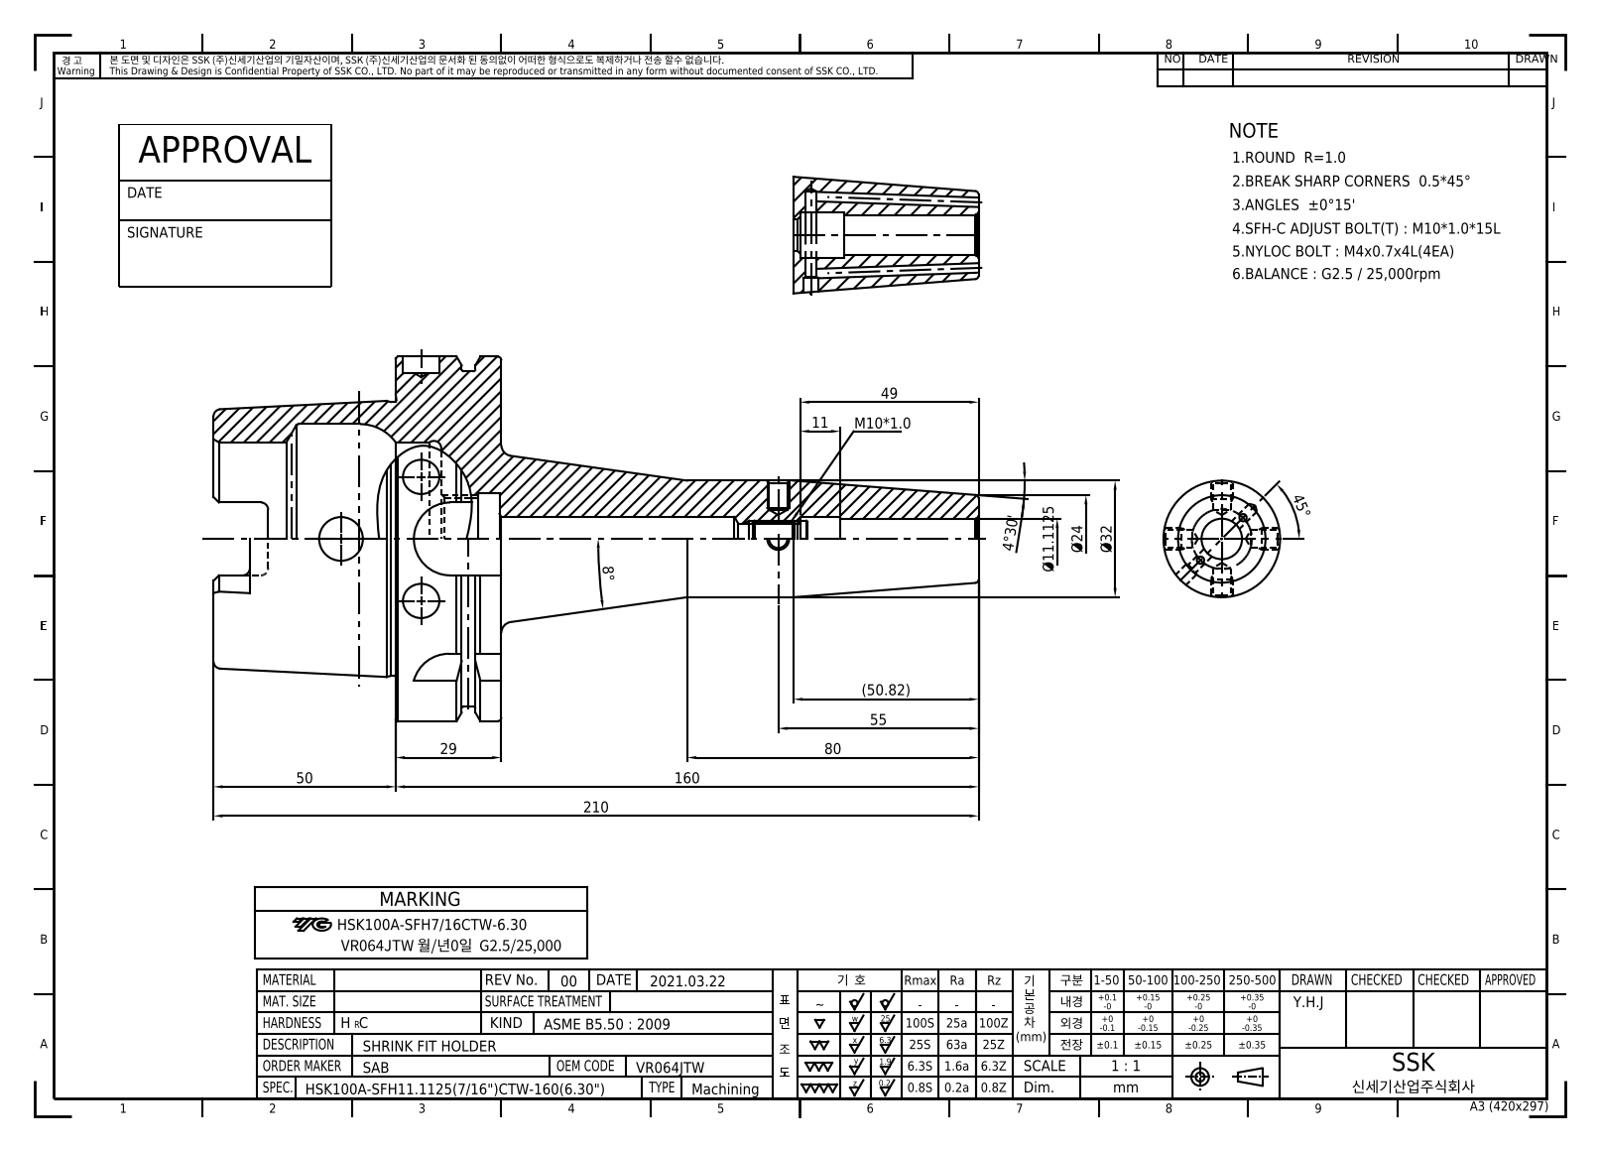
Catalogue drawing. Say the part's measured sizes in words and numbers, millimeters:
The part is named "LO-HSK100A-SFH11.1125CTW-160". Its 3-D file was written by "Autodesk Inventor 2022 (AUTOMOTIVE_DESIGN)". It is 1 solid with 120 faces: 38 planar, 37 cylindrical and 45 other. Overall it measures 210 by 100 by 100 millimeters. Its volume is 357 630 cubic millimeters and its surface area 67 505 square millimeters. Round holes: 2 of diameter 2, 2 of diameter 12, 1 of diameter 8.92, 1 of diameter 10, 1 of diameter 11.11, 1 of diameter 12.31, 1 of diameter 22.38, 1 of diameter 25, 1 of diameter 53, 1 of diameter 63. Round bosses or shafts: 1 of diameter 100, 1 of diameter 92, 1 of diameter 75.41, 1 of diameter 32. Partial cylindrical surfaces (rounded edges, fillets, slot ends): 6 of radius 2, 4 of radius 4.88, 4 of radius 10. The main face-to-face distances are 29, 12.5, 16.5, 62.5, 50, 79, 88, 78.5, 28.5, 16.
